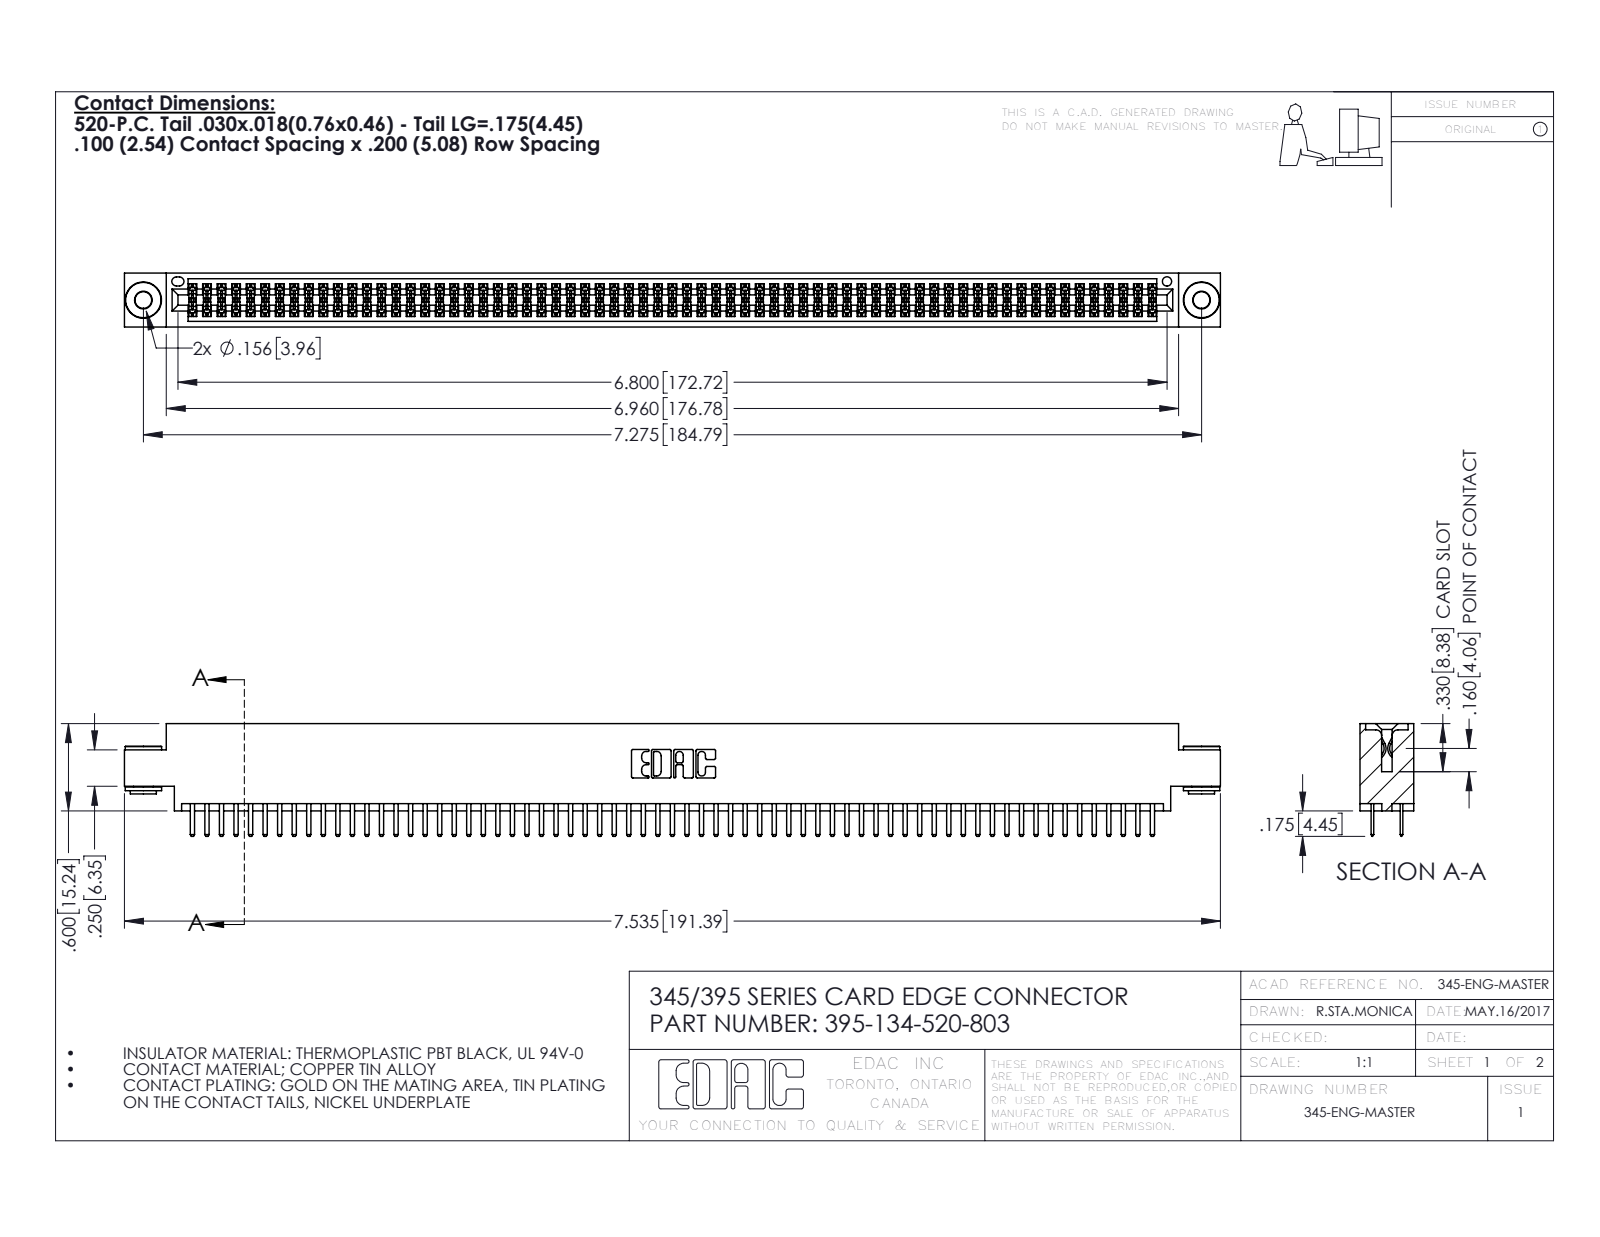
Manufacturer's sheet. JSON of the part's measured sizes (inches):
{"part_name": "345-292-001_345-293-120; 395-134-520-803; 345-250-002_345-250-002-102; 345 Part_0.170 Offset - 0.156 Dia-TH", "step_written_by": "SolidWorks 2016 (CONFIG_CONTROL_DESIGN)", "units": "inches", "bodies": {"solids": 137, "faces": 7404, "planar": 4784, "cylindrical": 2612, "other": 8}, "overall_size": [7.535, 0.775, 0.37], "volume_in3": 1.139, "surface_area_in2": 43.87, "round_holes": [[0.116, 2], [0.156, 2], [0.064, 1]], "round_bosses_or_shafts": [[0.25, 2], [0.18, 2], [0.136, 2]], "partial_cylinders_radius": [[0.006, 201], [0.01, 138], [0.01, 22], [0.007, 6], [0.031, 6], [0.026, 3], [0.014, 2], [0.019, 2]], "face_to_face_distances": [0.072, 0.298, 0.2, 0.37, 0.098, 0.272, 0.025, 0.225, 0.022, 0.072], "hole_center_spacings": [0.27, 7.039, 7.275]}
